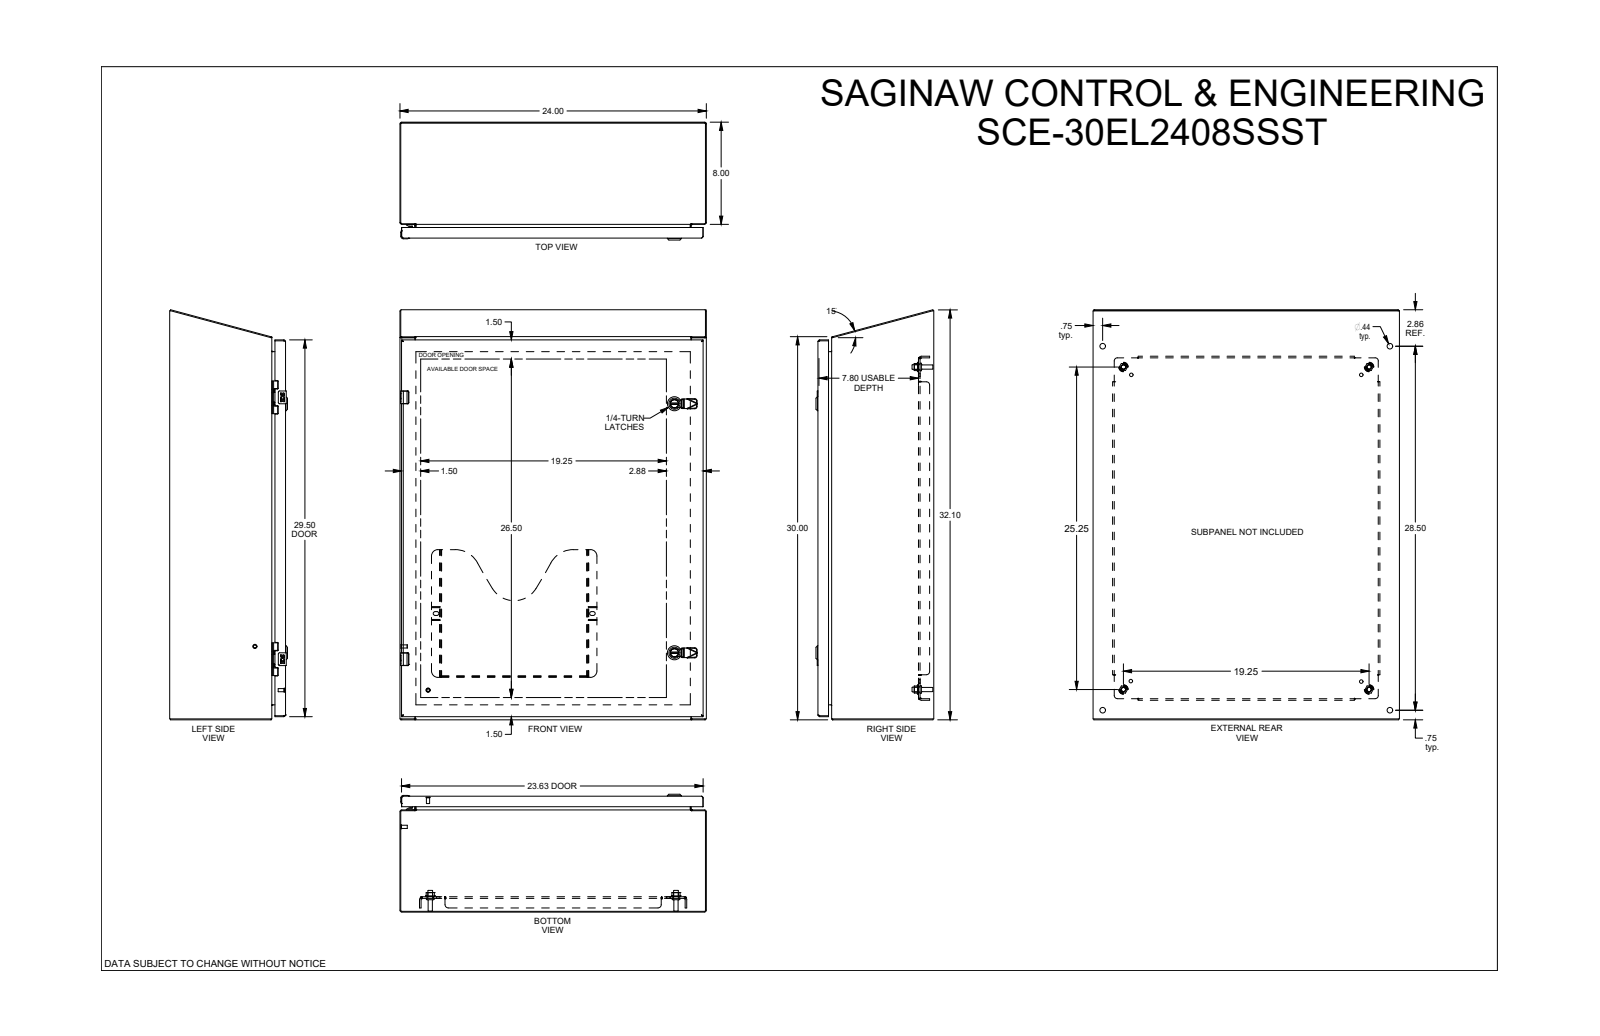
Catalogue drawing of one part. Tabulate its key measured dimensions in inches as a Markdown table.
| quantity | value |
| --- | --- |
| part name | SCE-30EL2408SSST |
| STEP written by | SolidWorks 2019 (CONFIG_CONTROL_DESIGN) |
| units | inches |
| bodies | 0 solids, 2844 faces (1311 planar, 759 cylindrical, 774 other) |
| overall size | 32.106 × 24 × 9.23 |
| round holes (diameter × count) | 0.172 × 4, 0.205 × 4, 0.244 × 4, 0.266 × 4, 0.281 × 4, 0.367 × 4, 0.375 × 4, 0.437 × 4, 0.5 × 4, 0.156 × 2, 0.197 × 2, 0.218 × 2 |
| round bosses / shafts (diameter × count) | 0.17 × 6, 0.366 × 4, 0.332 × 4, 0.25 × 4, 0.248 × 4, 0.196 × 3, 1.102 × 2, 0.866 × 2 |
| partial cylindrical surfaces (radius × count) | 0.012 × 56, 0.015 × 32, 0.01 × 28, 0.04 × 23, 0.02 × 20, 0.029 × 12, 0.06 × 11, 0.07 × 10 |
| main face-to-face distances | 0.075, 0.075, 8.998, 8.923, 9.073, 8.998, 1.2, 7.873, 1, 0.125 |
| hole center spacings | 20.5, 0.985, 0.02, 0.875, 2.298, 4.493, 20.938, 26.924 |
